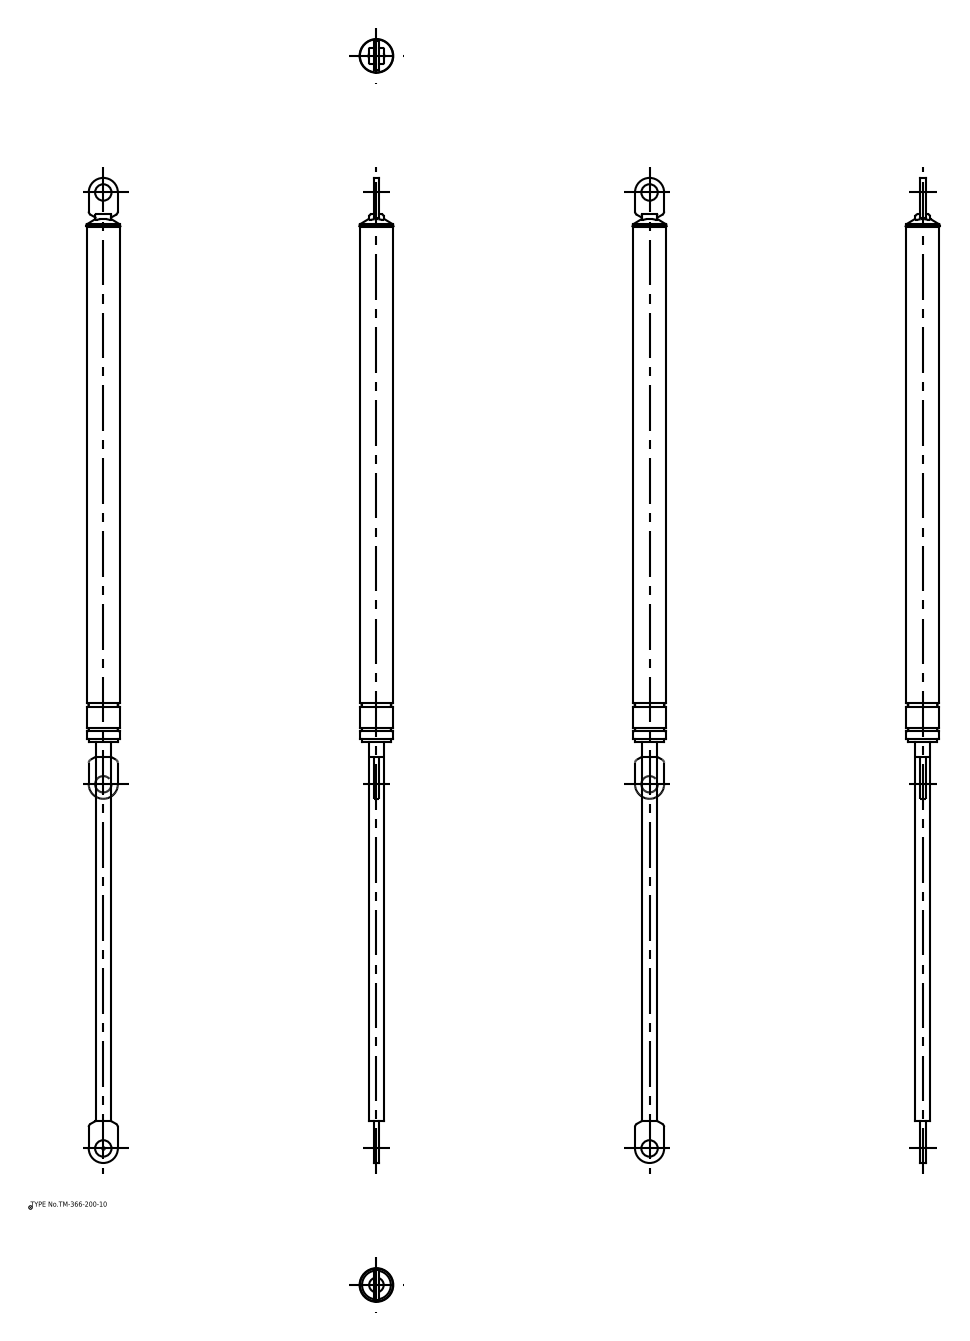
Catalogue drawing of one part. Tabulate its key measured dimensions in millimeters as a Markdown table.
| quantity | value |
| --- | --- |
| part name | TM_366_200_10; TM_366_200_10_div |
| STEP written by | spGate 16.7.1 (AUTOMOTIVE_DESIGN) |
| units | millimeters |
| bodies | 2 solids, 89 faces (35 planar, 36 cylindrical, 18 other) |
| overall size | 541 × 18.5 × 18.5 |
| volume | 84 810 mm³ |
| surface area | 23 675 mm² |
| round holes (diameter × count) | 9 × 2 |
| round bosses / shafts (diameter × count) | 18 × 1, 15.8 × 1, 8 × 1 |
| partial cylindrical surfaces (radius × count) | 0.3 × 8, 2 × 4, 0.5 × 2, 1.15 × 2, 8 × 2 |
| main face-to-face distances | 3.2, 16, 1.7, 208, 209.7, 3.7, 12.3, 13.5, 1.8, 2.4 |
| hole center spacings | 525 |
